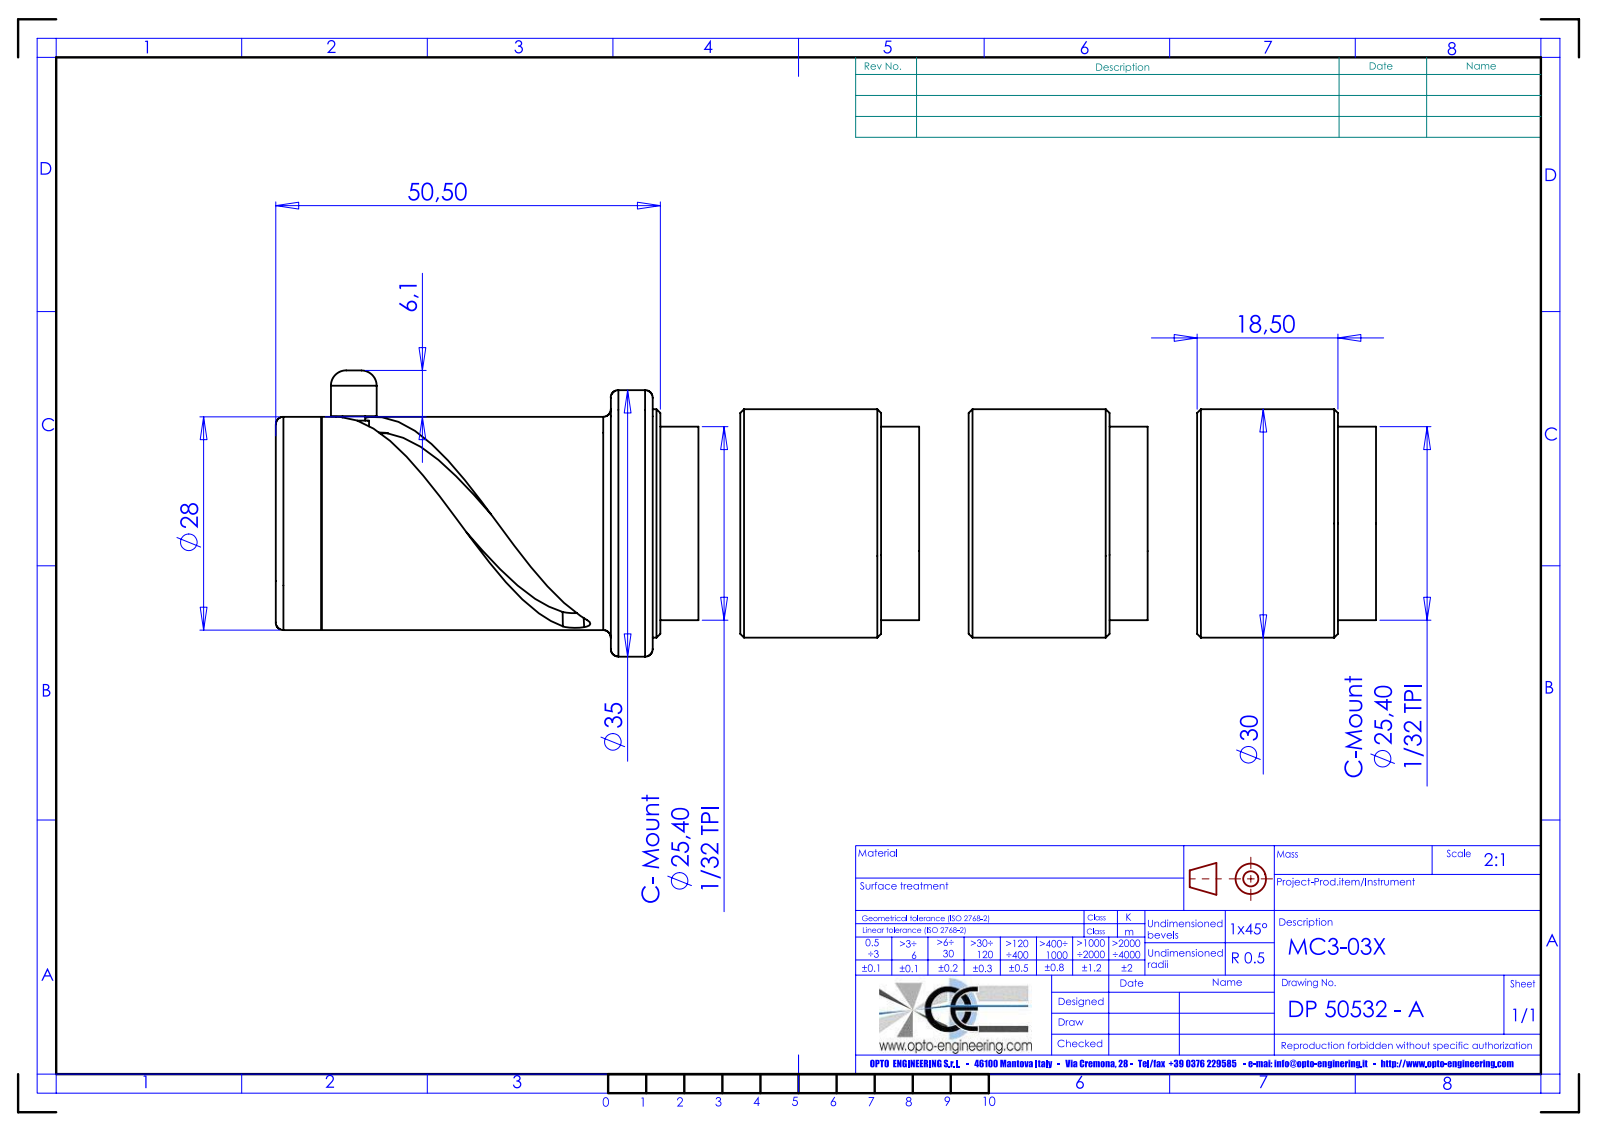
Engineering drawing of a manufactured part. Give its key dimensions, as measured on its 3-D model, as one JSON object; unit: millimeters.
{"part_name": "MC0.00X", "step_written_by": "SolidWorks 2012 (AUTOMOTIVE_DESIGN)", "units": "millimeters", "bodies": {"solids": 0, "faces": 99, "planar": 17, "cylindrical": 42, "other": 40}, "overall_size": [111, 37.15, 35], "round_holes": [[2, 2], [9, 1], [13, 1], [20, 1], [22, 1], [24, 1], [30.4, 1]], "round_bosses_or_shafts": [[28, 2], [35, 1], [30, 1], [25.4, 1], [24, 1], [6, 1], [4, 1]], "face_to_face_distances": [18.5, 43.5, 37, 38, 63, 81.5, 0.57, 63.57, 82.07, 5.5], "hole_center_spacings": [6, 0.44, 5.56, 6.44, 12]}
